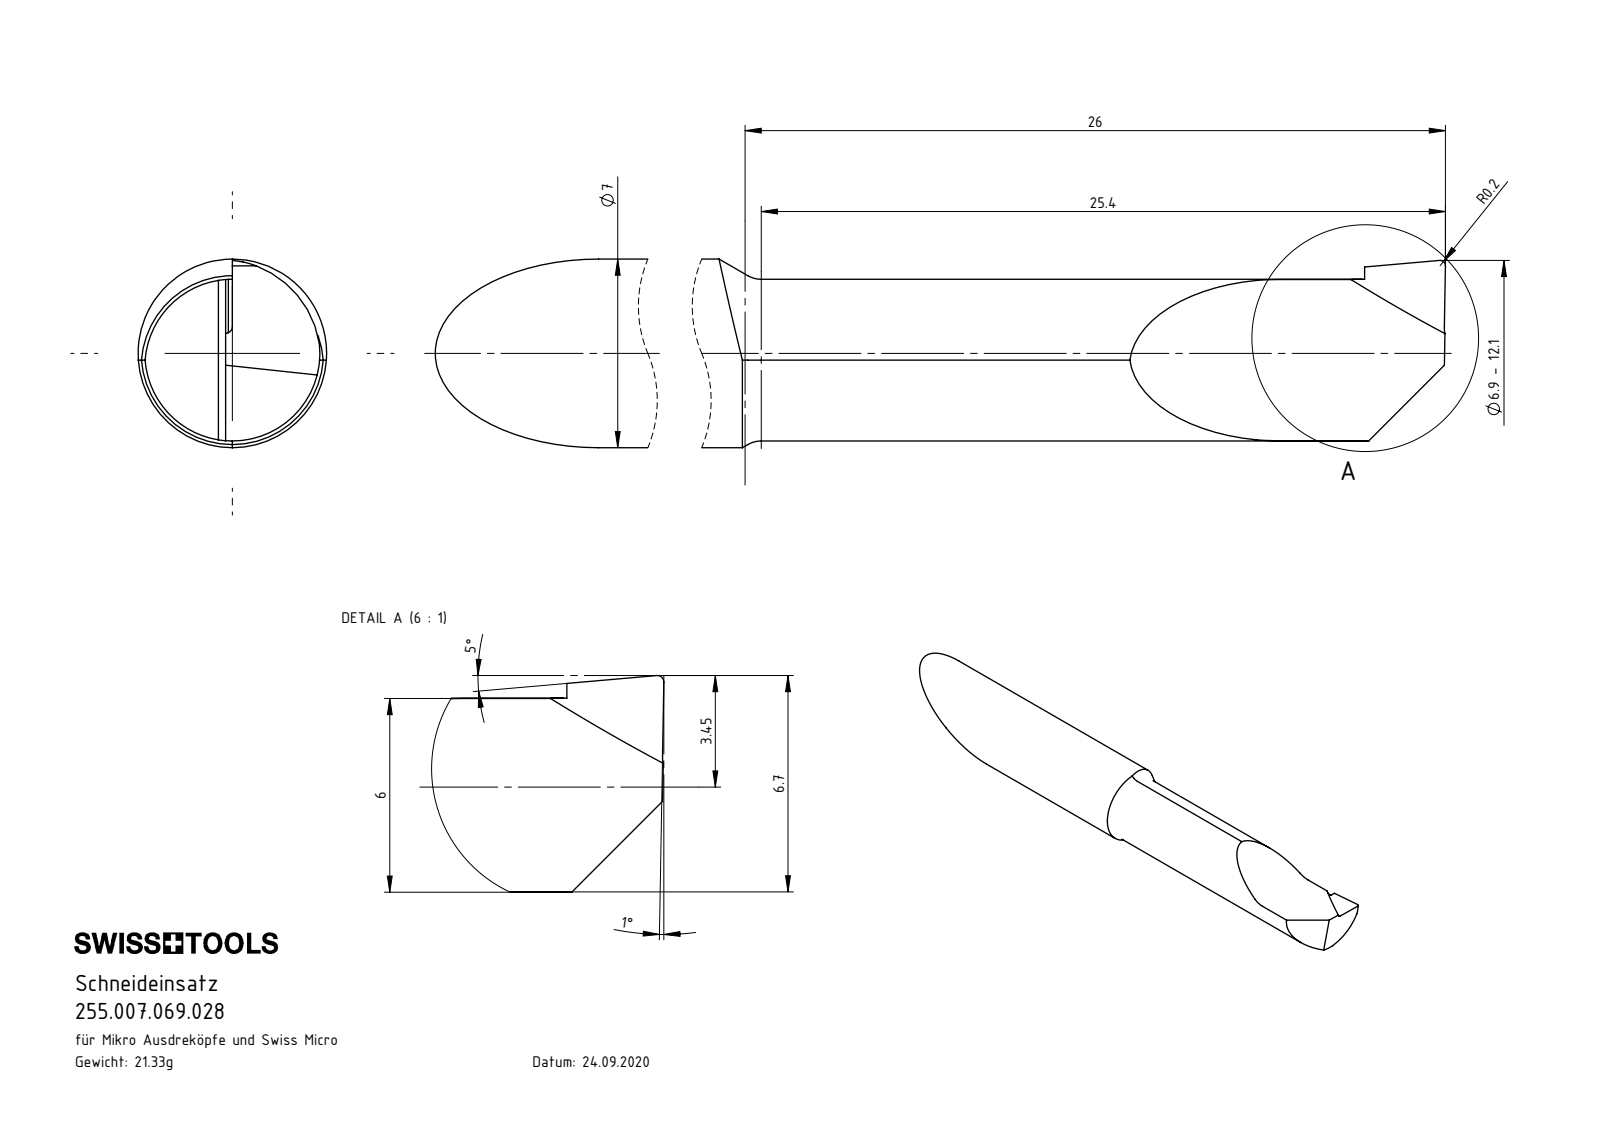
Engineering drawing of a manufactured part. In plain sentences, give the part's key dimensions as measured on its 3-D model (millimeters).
The part is named "A07.0345.25.69.20_YR". Its 3-D file was written by "SolidWorks 2017 (AUTOMOTIVE_DESIGN)". It is 1 solid with 27 faces: 9 planar, 6 cylindrical and 12 other. Overall it measures 53.31 by 7 by 7 millimeters. Its volume is 1 471 cubic millimeters and its surface area 1 037 square millimeters. Round bosses or shafts: 1 of diameter 7. Partial cylindrical surfaces (rounded edges, fillets, slot ends): 2 of radius 3.25, 1 of radius 2. The main face-to-face distances are 20.58.
